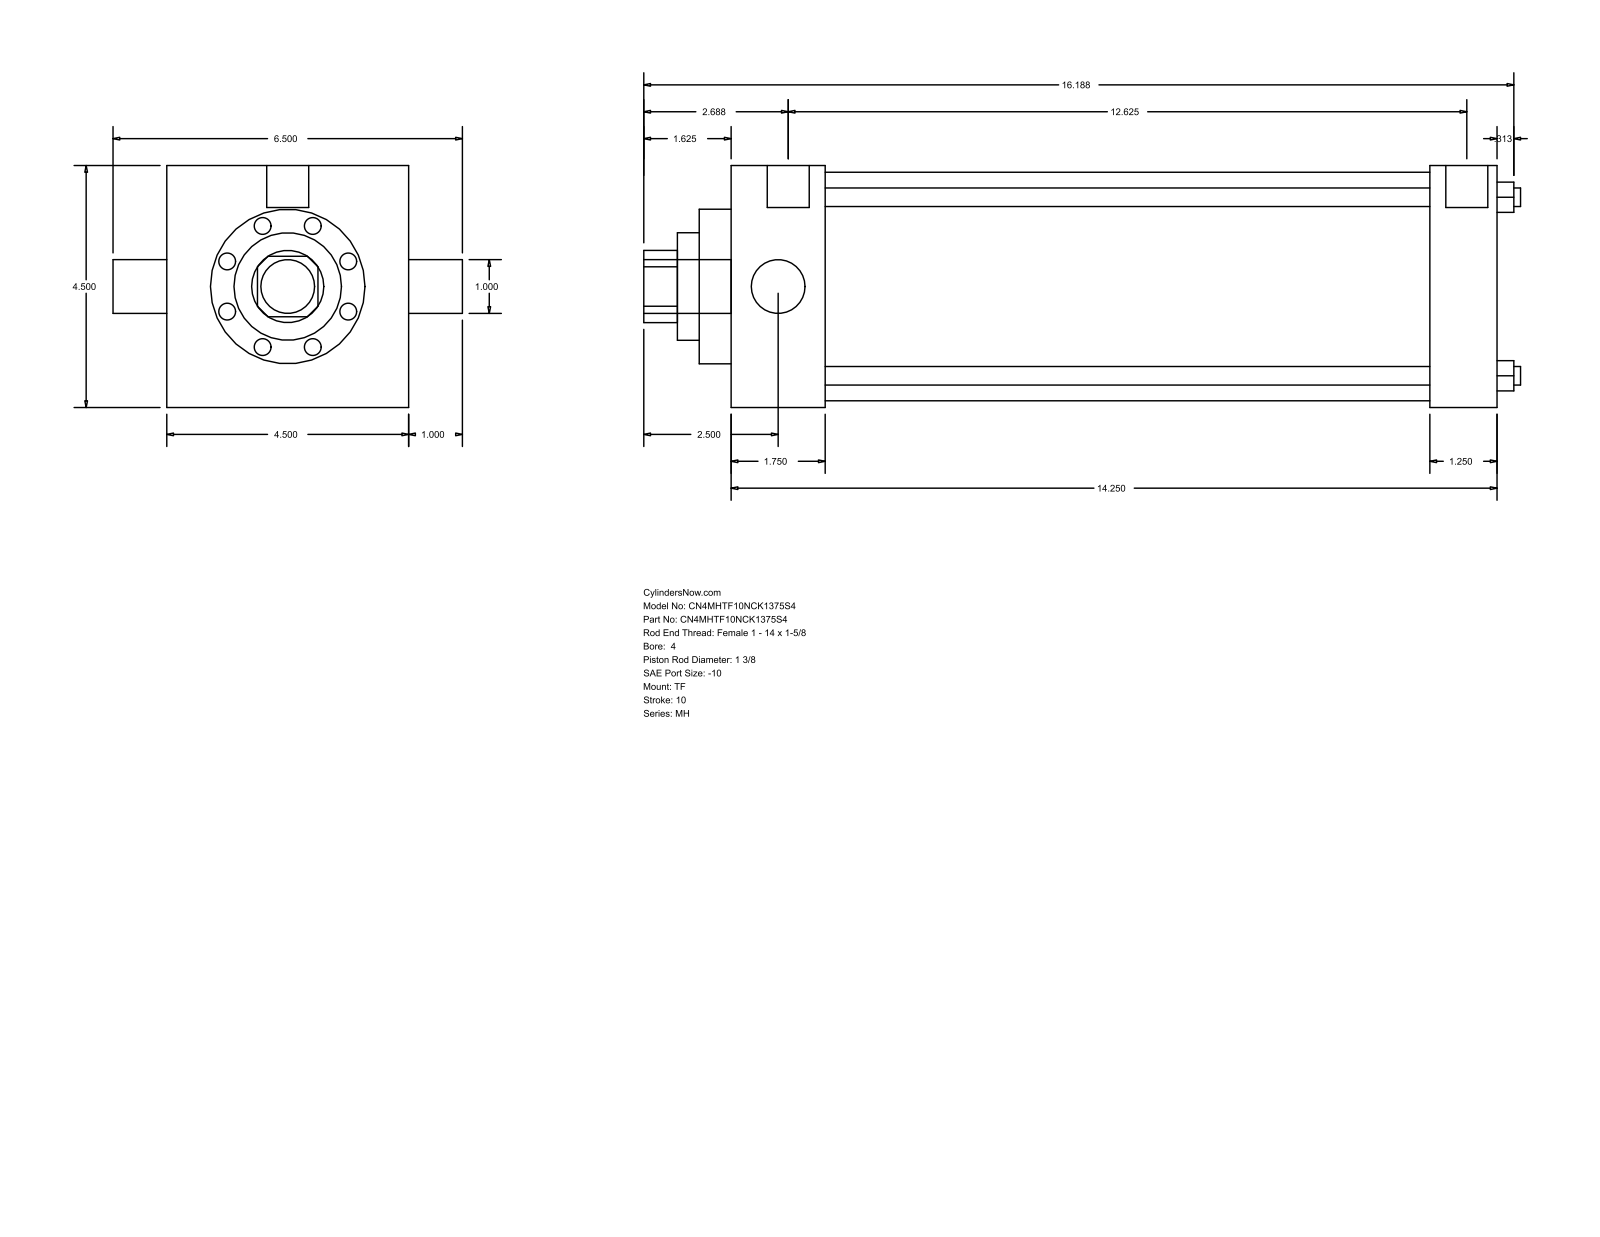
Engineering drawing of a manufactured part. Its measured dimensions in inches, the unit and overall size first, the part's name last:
Units: inches
Overall size (bounding box): 16.313 × 6.5 × 4.5
Round holes (diameter × count): ⌀0.345 ×4, ⌀1 ×1, ⌀1.375 ×1, ⌀2 ×1, ⌀2.875 ×1, ⌀4.25 ×1
Round bosses / shafts (diameter × count): ⌀0.344 ×3, ⌀0.781 ×2, ⌀1 ×1
Partial cylindrical surfaces — rounded edges, fillets, slot ends (radius × count): R0.672 ×1
Main face-to-face distances: 4.5, 14.25, 1.75, 12.5, 13, 11.25, 1.25, 0.594, 2.344, 13.594
Hole centre spacings: 2.347, 3.32, 4.695
Bodies: 0 solids, 86 faces (61 planar, 25 cylindrical, 0 other)
Part name (STEP PRODUCT): MH_TF__0400_1.375
STEP written by: GSSL Pune (CONFIG_CONTROL_DESIGN)
